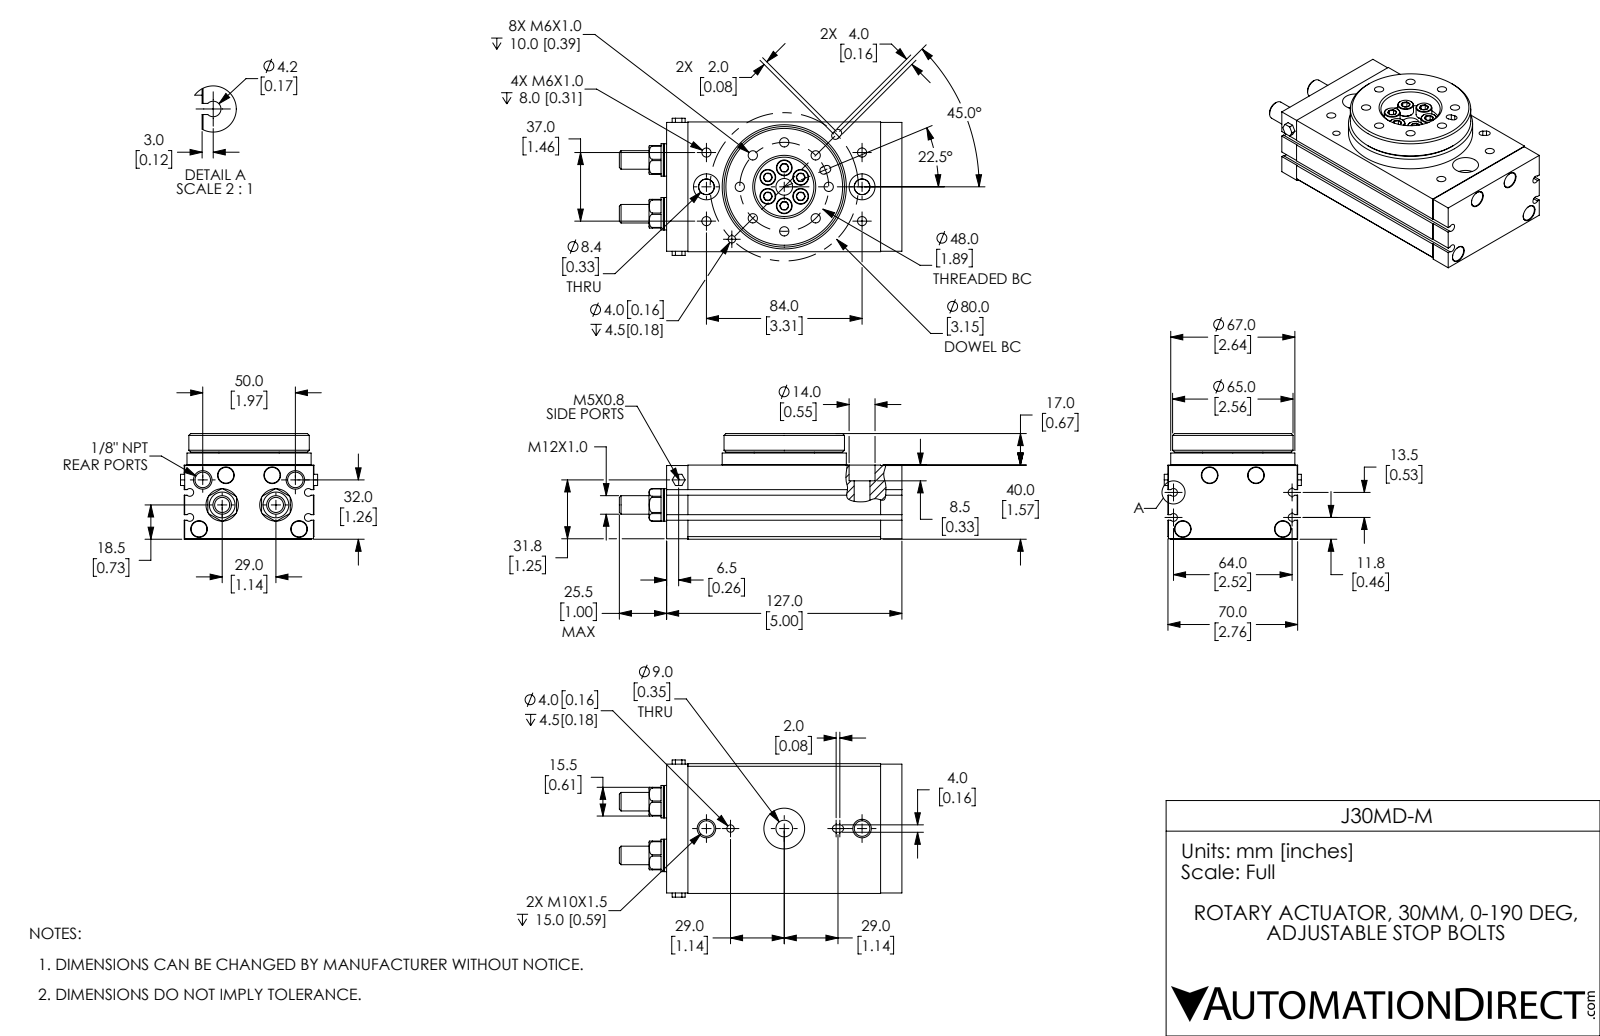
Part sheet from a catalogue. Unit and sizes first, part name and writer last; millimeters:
Units: millimetres
Overall size (bounding box): 152.5 × 74 × 57
Round holes (diameter × count): ⌀5 ×12, ⌀9 ×5, ⌀4.92 ×4, ⌀8.38 ×4, ⌀8.5 ×2, ⌀14 ×2, ⌀22 ×1, ⌀32 ×1, ⌀32.5 ×1
Round bosses / shafts (diameter × count): ⌀8.5 ×10, ⌀5 ×6, ⌀3.96 ×6, ⌀17.5 ×2, ⌀10 ×2, ⌀67 ×1, ⌀65 ×1
Partial cylindrical surfaces — rounded edges, fillets, slot ends (radius × count): R2 ×6, R2.1 ×4
Main face-to-face distances: 40, 70, 39.75, 7, 47, 0.5, 6.5, 46.5, 10, 10.5
Hole centre spacings: 18.37, 24, 33.94, 44.35, 10.25, 18.5, 20.86, 25.08
Volume: 386 249 mm³ · Surface area: 63 712 mm²
Bodies: 8 solids, 649 faces (191 planar, 318 cylindrical, 140 other)
Part name (STEP PRODUCT): J30MD-M; J30MD-M_M5_91290A221; J30MD-M_table; J30MD-M_body2
STEP written by: SolidWorks 2017 (AUTOMOTIVE_DESIGN)
